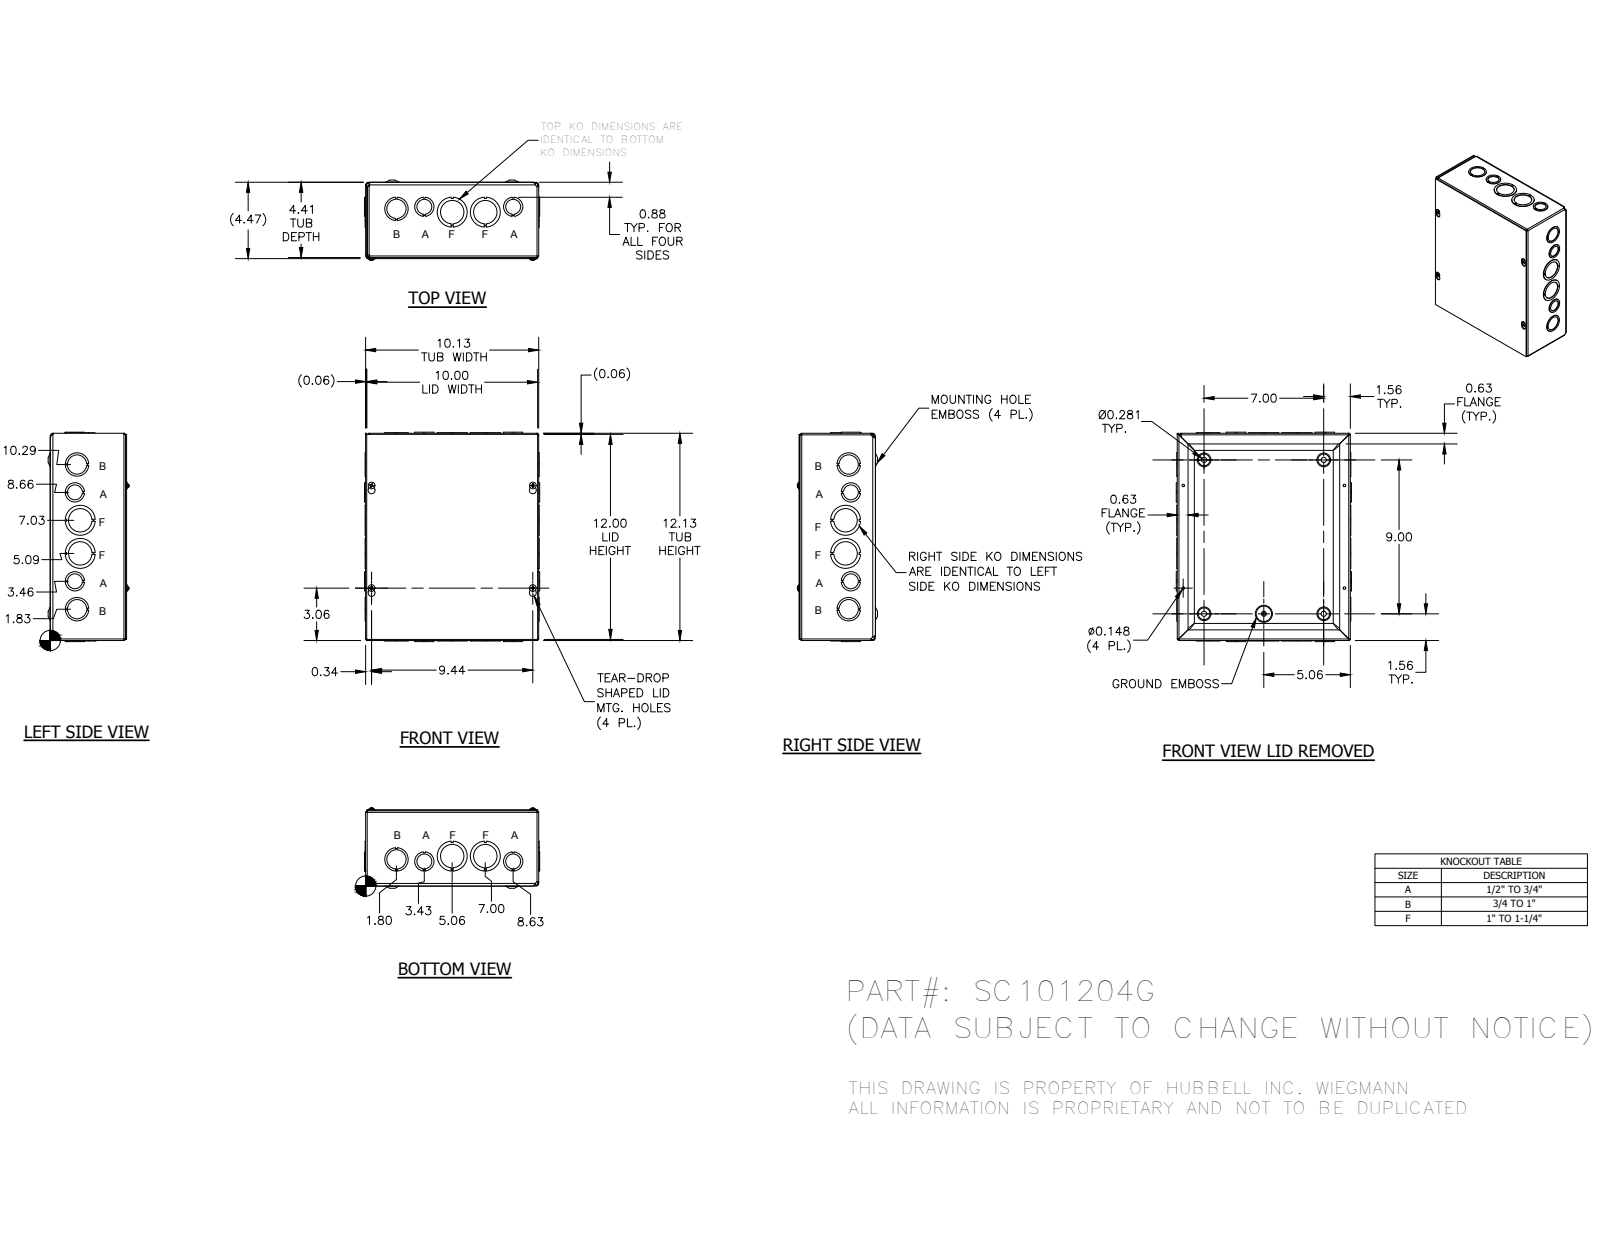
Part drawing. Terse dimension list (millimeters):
name: SC1012GBKP; SC101204GWRA; SC1012GLID; 34056 (+1 more)
written by: Autodesk Inventor 2014 (AUTOMOTIVE_DESIGN)
unit: mm
bodies: 22 solids, 974 faces (618 planar, 205 cylindrical, 151 other)
size: 311.12 × 260.32 × 119.2
holes: 7× ⌀28.57, 7× ⌀34.92, 4× ⌀3.76, 4× ⌀7.62, 4× ⌀22.22, 4× ⌀44.45, 1× ⌀4.19
bosses: 4× ⌀9.75, 4× ⌀4.17, 1× ⌀5.8
rounds: 8× R0.79, 8× R2.37, 4× R1.4, 4× R1.57, 4× R2.38, 4× R2.79, 4× R2.97, 4× R3.15
face distances: 1.57, 110.32, 111.89, 1.59, 111.91, 113.48, 306.4, 1.58, 257.18, 255.6
hole spacings: 49.09, 193, 282.61, 42.15, 91.03, 132.17, 41.52, 82.94
